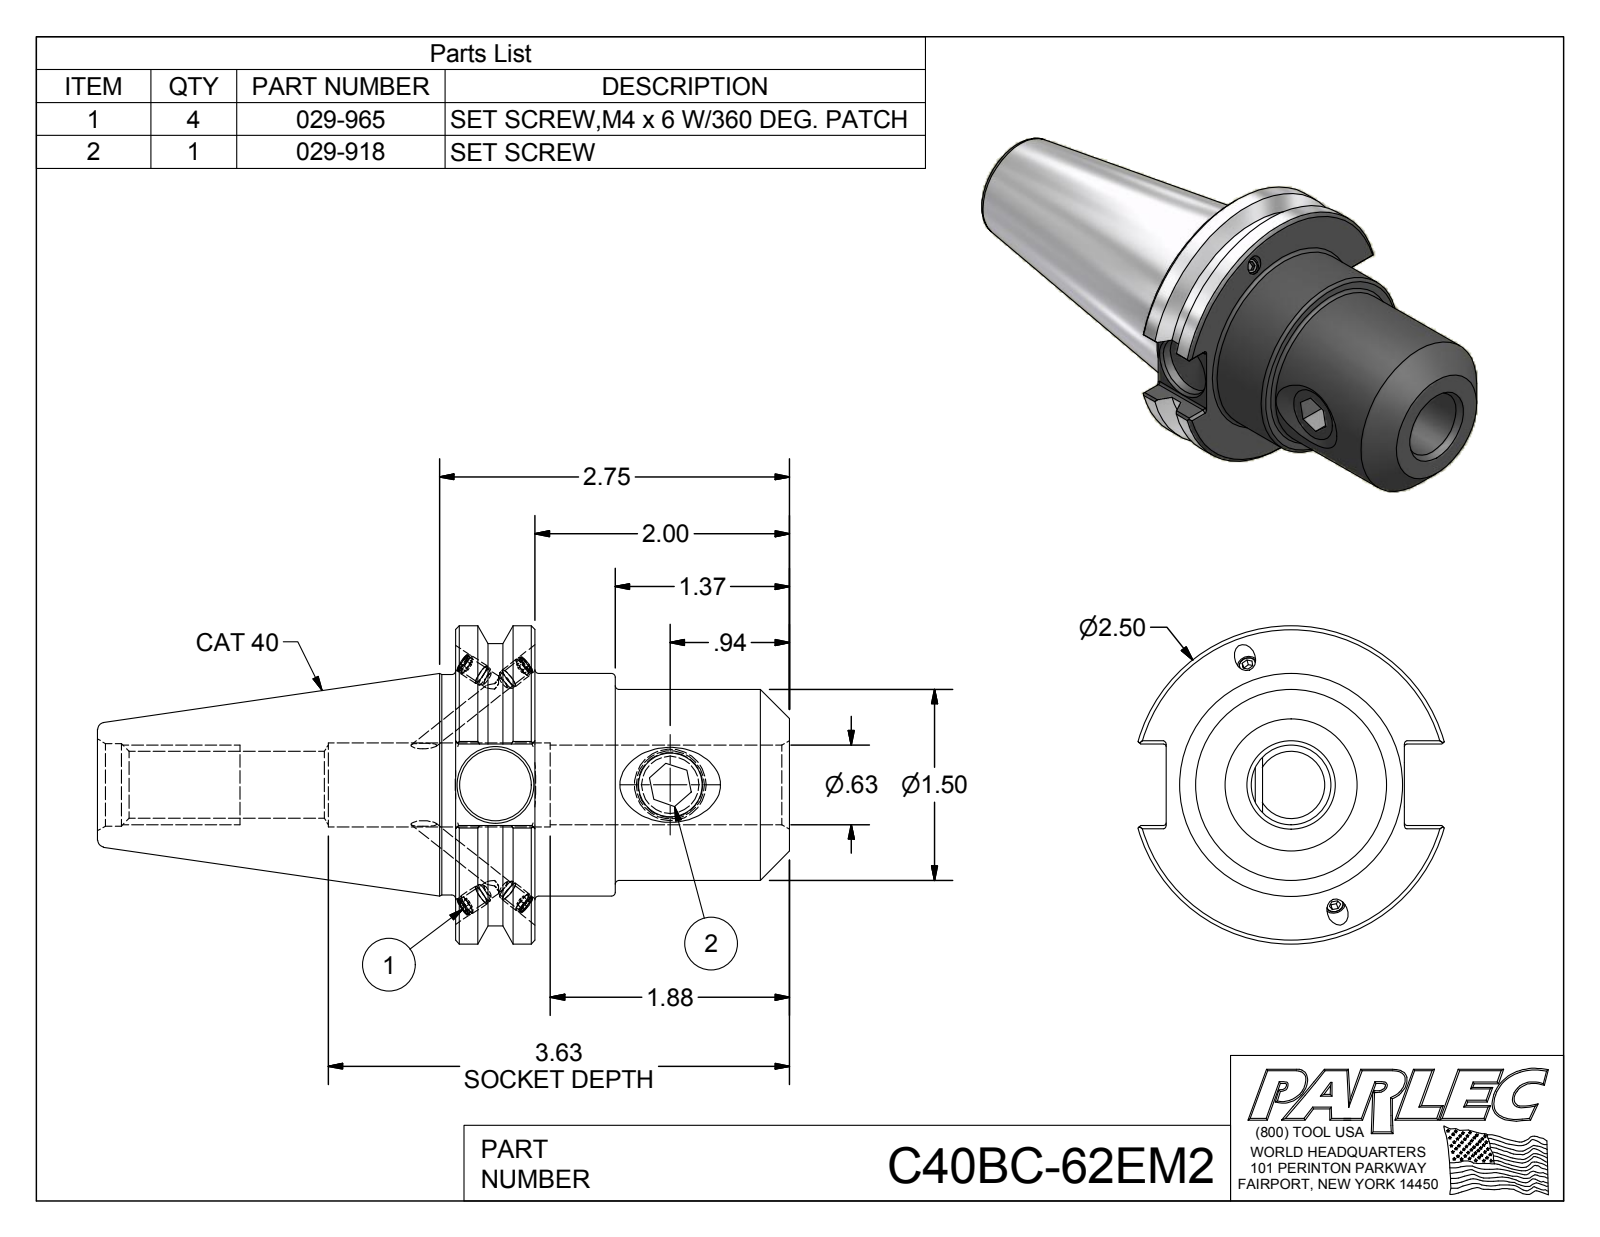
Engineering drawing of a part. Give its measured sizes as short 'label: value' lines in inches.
name: C40BC-62EM2; C40BC-62EM2-1; 029-918; 029-965
written by: Autodesk Inventor 2012 (AUTOMOTIVE_DESIGN)
unit: in
bodies: 6 solids, 142 faces (66 planar, 36 cylindrical, 40 other)
size: 5.438 × 2.5 × 2.417
volume: 9.102 in³; area: 48.38 in²
holes: 4× ⌀0.13, 4× ⌀0.161, 1× ⌀0.502, 1× ⌀0.527, 1× ⌀0.563, 1× ⌀0.625, 1× ⌀0.648, 1× ⌀0.66
bosses: 4× ⌀0.165, 4× ⌀0.157, 1× ⌀2.5, 1× ⌀2.219, 1× ⌀1.75, 1× ⌀1.5, 1× ⌀0.563
face distances: 0.625, 2.625, 2, 1.255, 0.63, 1.37, 0.64, 2.813, 3.437, 4.067
hole spacings: 1.372
